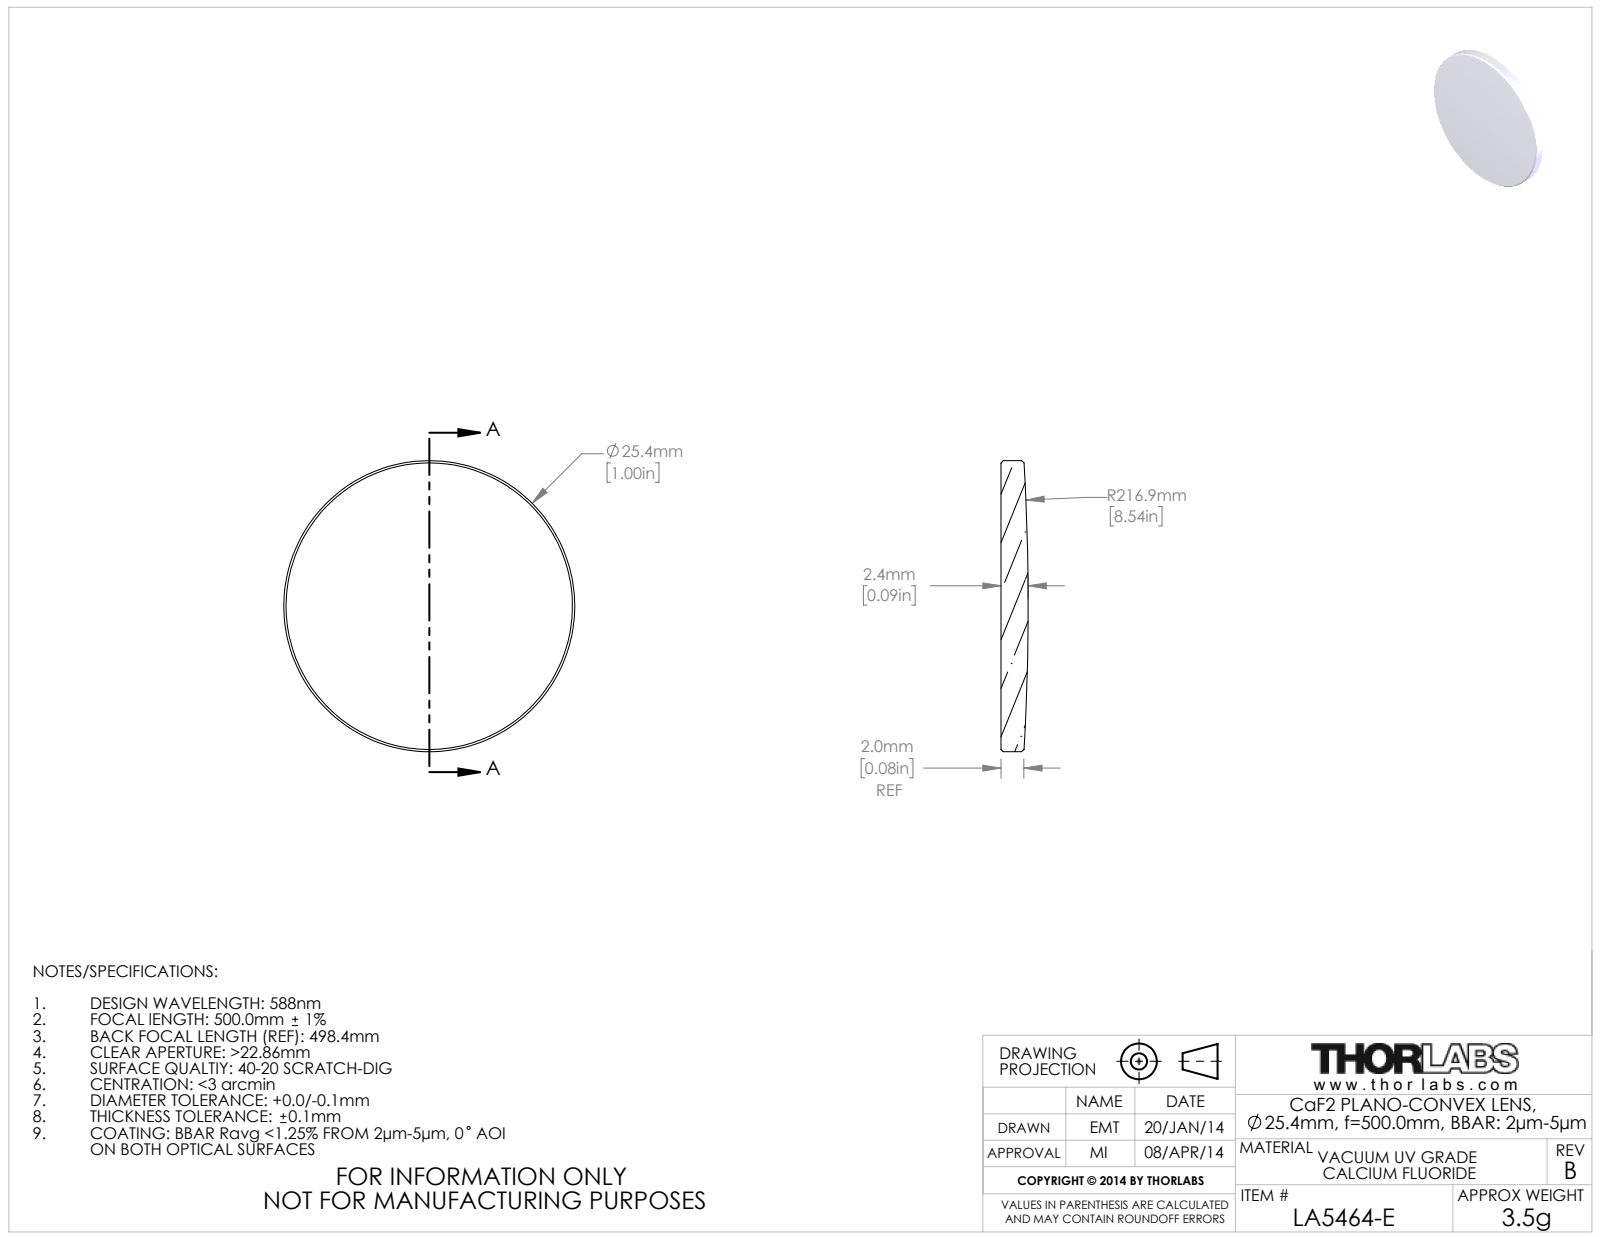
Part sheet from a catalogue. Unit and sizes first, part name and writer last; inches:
Units: inches
Overall size (bounding box): 1 × 1 × 0.093
Round bosses / shafts (diameter × count): ⌀1 ×1
Volume: 0.067 in³ · Surface area: 1.79 in²
Bodies: 1 solid, 9 faces (1 planar, 2 cylindrical, 6 other)
Part name (STEP PRODUCT): 20138-E0W
STEP written by: SolidWorks 2018 (CONFIG_CONTROL_DESIGN)
